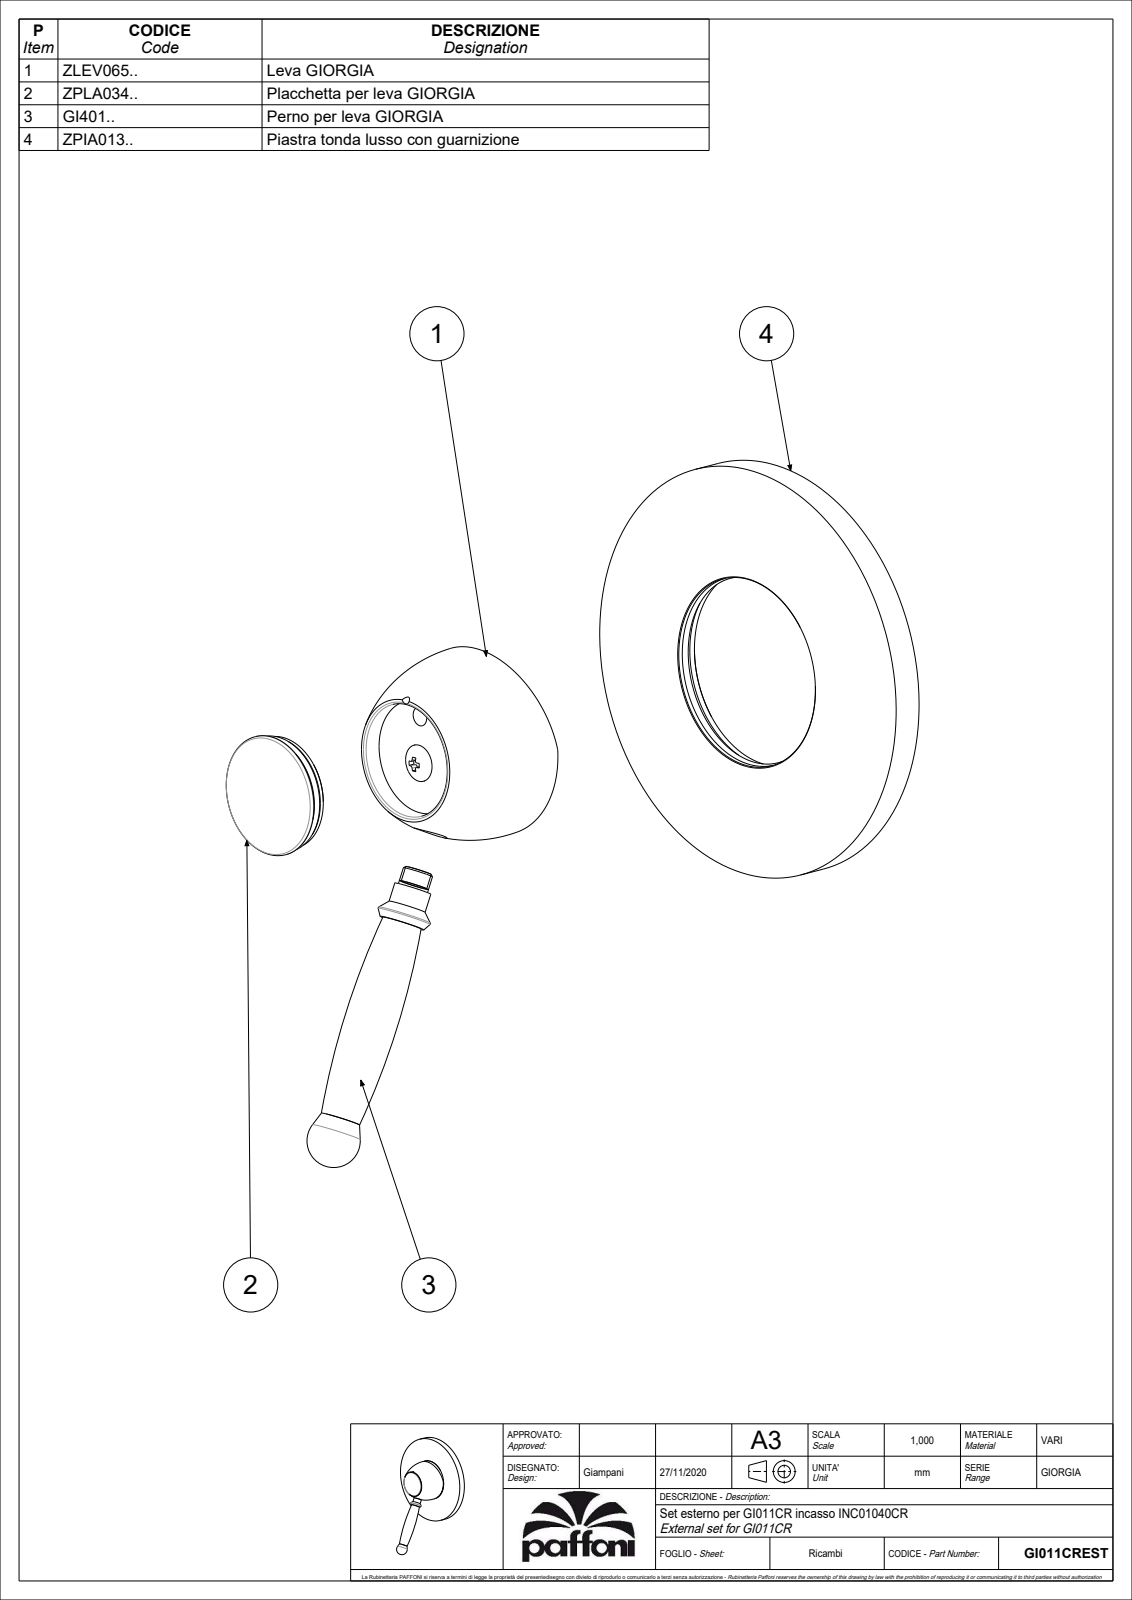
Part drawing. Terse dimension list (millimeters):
name: GI011CREST
written by: CREO PARAMETRIC BY PTC INC, 2020044 (CONFIG_CONTROL_DESIGN)
unit: mm
bodies: 3 solids, 211 faces (113 planar, 46 cylindrical, 52 other)
size: 146.65 × 110 × 67.88
volume: 52 594 mm³; area: 41 968 mm²
holes: 2× ⌀5, 1× ⌀12, 1× ⌀30.3, 1× ⌀50.7, 1× ⌀52.7, 1× ⌀56.6, 1× ⌀105
bosses: 1× ⌀110, 1× ⌀59.7, 1× ⌀32, 1× ⌀29.9, 1× ⌀27, 1× ⌀17.5, 1× ⌀9.9, 1× ⌀9.8
rounds: 4× R0.5, 1× R2, 1× R3.5, 1× R24.35
face distances: 7, 35.22, 28.22, 1.5, 5.5, 33.72, 23, 7.52, 6.02, 0.52
hole spacings: 1.6, 11, 12.6
